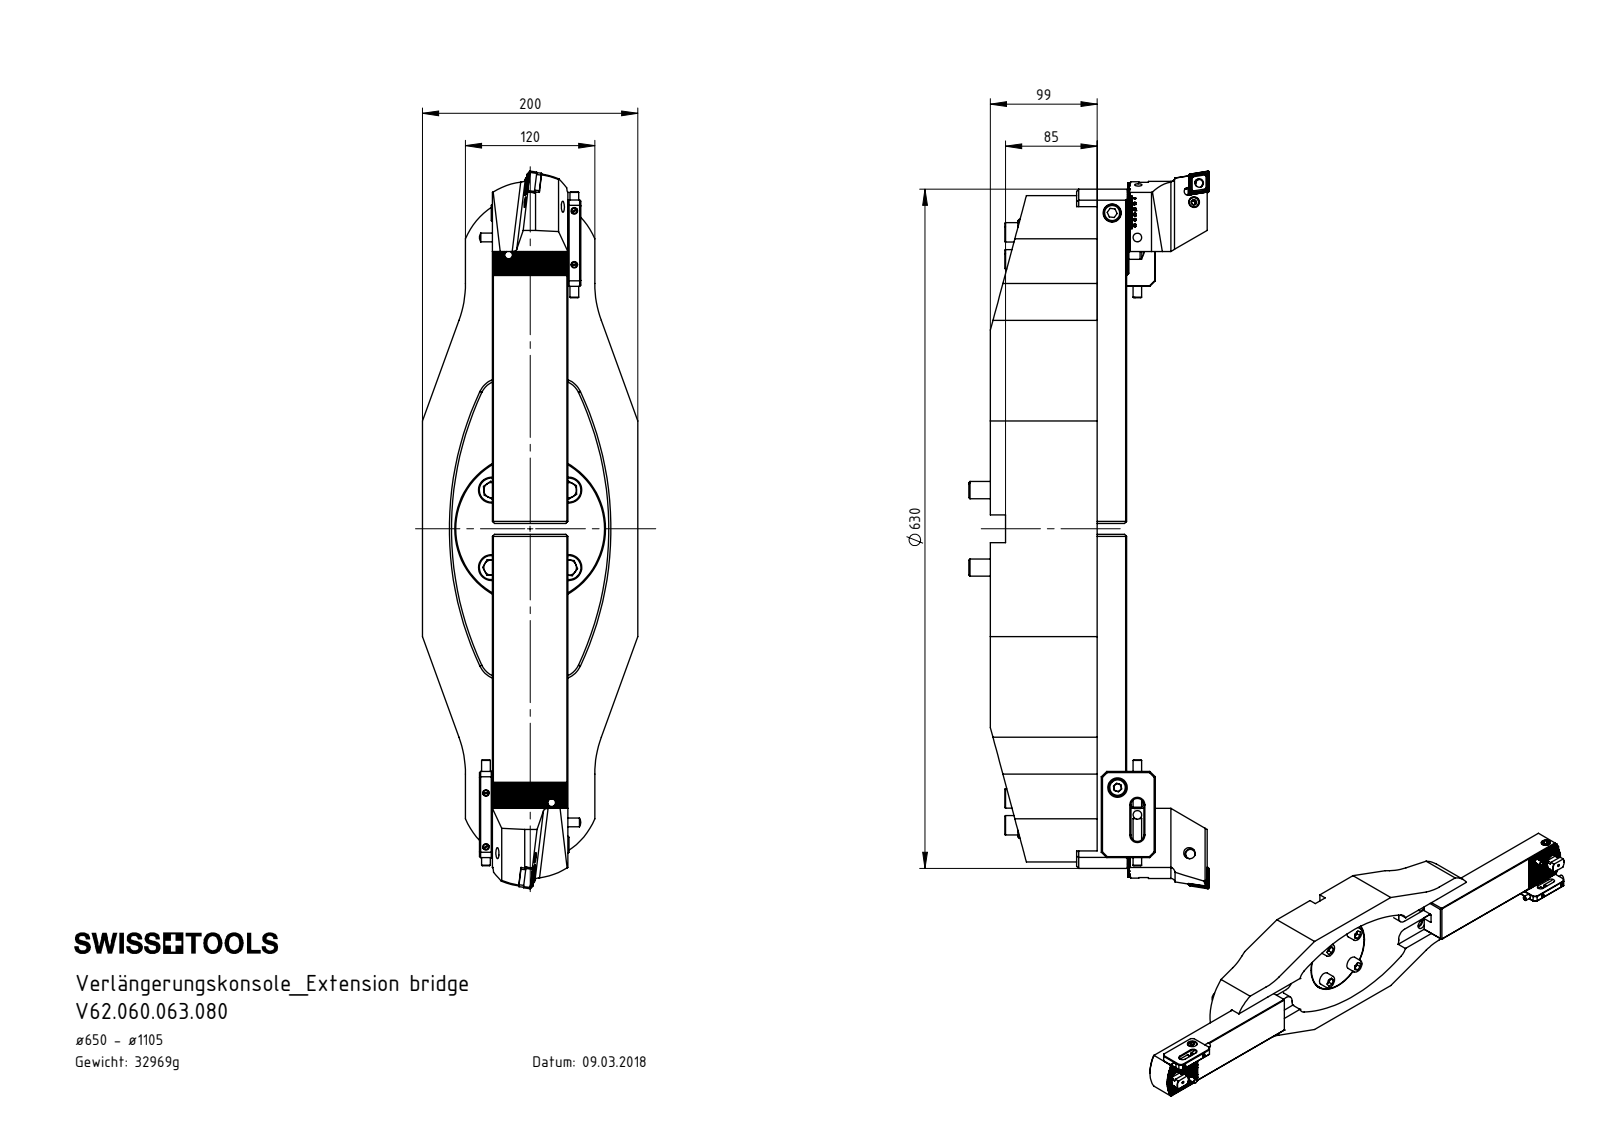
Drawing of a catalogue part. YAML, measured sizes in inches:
part_name: "VK3-ER1.001.005_A; D60-VK3.063.080_B; ISO 4762 - M12 x 80; D60.VK3.063.080 (+3 more)"
step_written_by: "SolidWorks 2017 (AUTOMOTIVE_DESIGN)"
units: inches
bodies: {solids: 40, faces: 678, planar: 374, cylindrical: 167, other: 137}
overall_size: [24.331, 7.874, 4.941]
volume: 391.8
surface_area: 889
round_holes:
  - {diameter: 0.512, count: 16}
  - {diameter: 0.709, count: 10}
  - {diameter: 0.472, count: 7}
  - {diameter: 0.669, count: 4}
  - {diameter: 2.362, count: 1}
  - {diameter: 5.512, count: 1}
round_bosses_or_shafts:
  - {diameter: 0.945, count: 16}
  - {diameter: 0.472, count: 7}
  - {diameter: 0.709, count: 6}
  - {diameter: 0.63, count: 4}
  - {diameter: 5.433, count: 1}
partial_cylinders:
  - {radius: 0.079, count: 12}
  - {radius: 0.866, count: 8}
  - {radius: 0.315, count: 4}
  - {radius: 0.394, count: 4}
  - {radius: 0.591, count: 4}
  - {radius: 3.937, count: 4}
  - {radius: 2.559, count: 2}
  - {radius: 11.811, count: 2}
face_to_face_distances: [2.362, 3.898, 1.535, 1.732, 1.102, 1.26, 2.795, 0.197, 2.165, 1.063]
hole_center_spacings: [0.984, 1.857, 1.575, 1.969, 2.521, 18.701, 18.767, 17.717]
